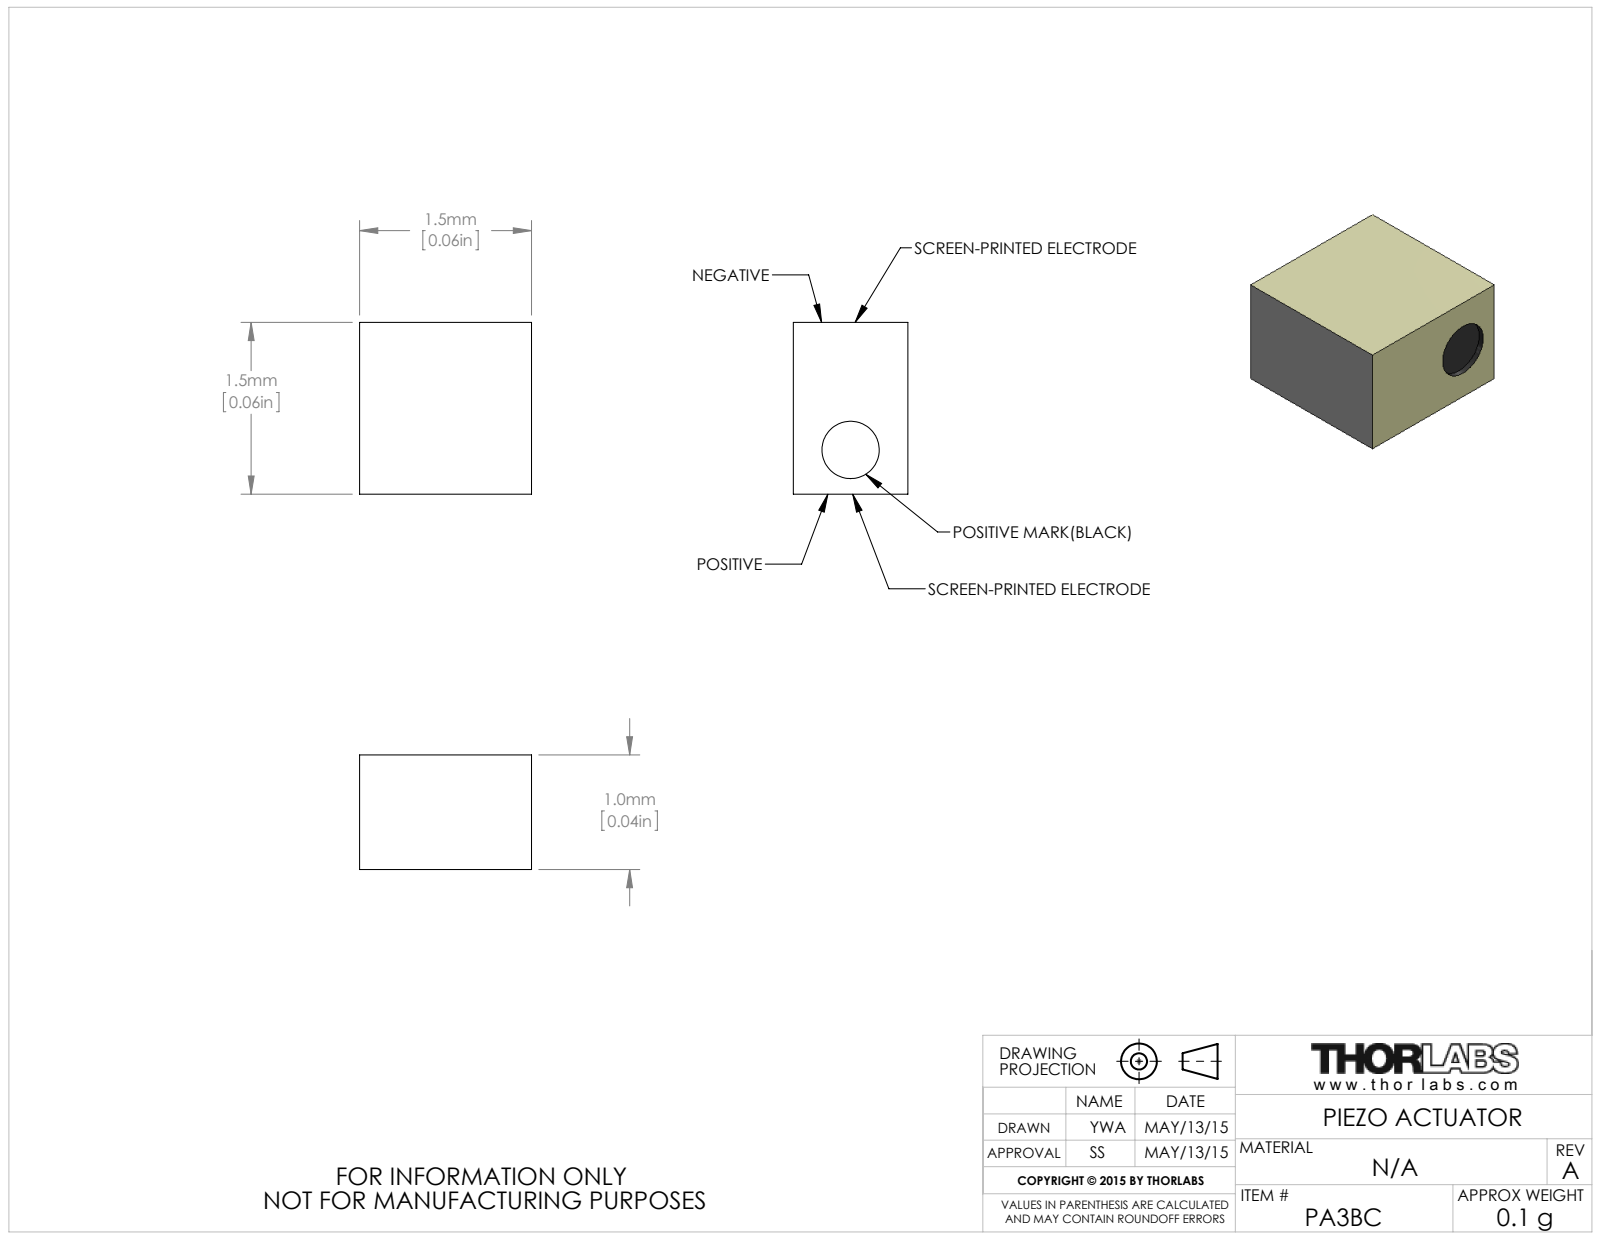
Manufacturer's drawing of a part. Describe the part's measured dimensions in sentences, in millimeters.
The part is named "CTN002515". Its 3-D file was written by "SolidWorks 2014 (AUTOMOTIVE_DESIGN)". It is 1 solid with 9 faces: 7 planar, 2 cylindrical and 0 other. Overall it measures 1.5 by 1.5 by 1 millimeters. Its volume is 2 cubic millimeters and its surface area 11 square millimeters. Round holes: 1 of diameter 0.5. The main face-to-face distances are 1.5, 1, 1.45.
